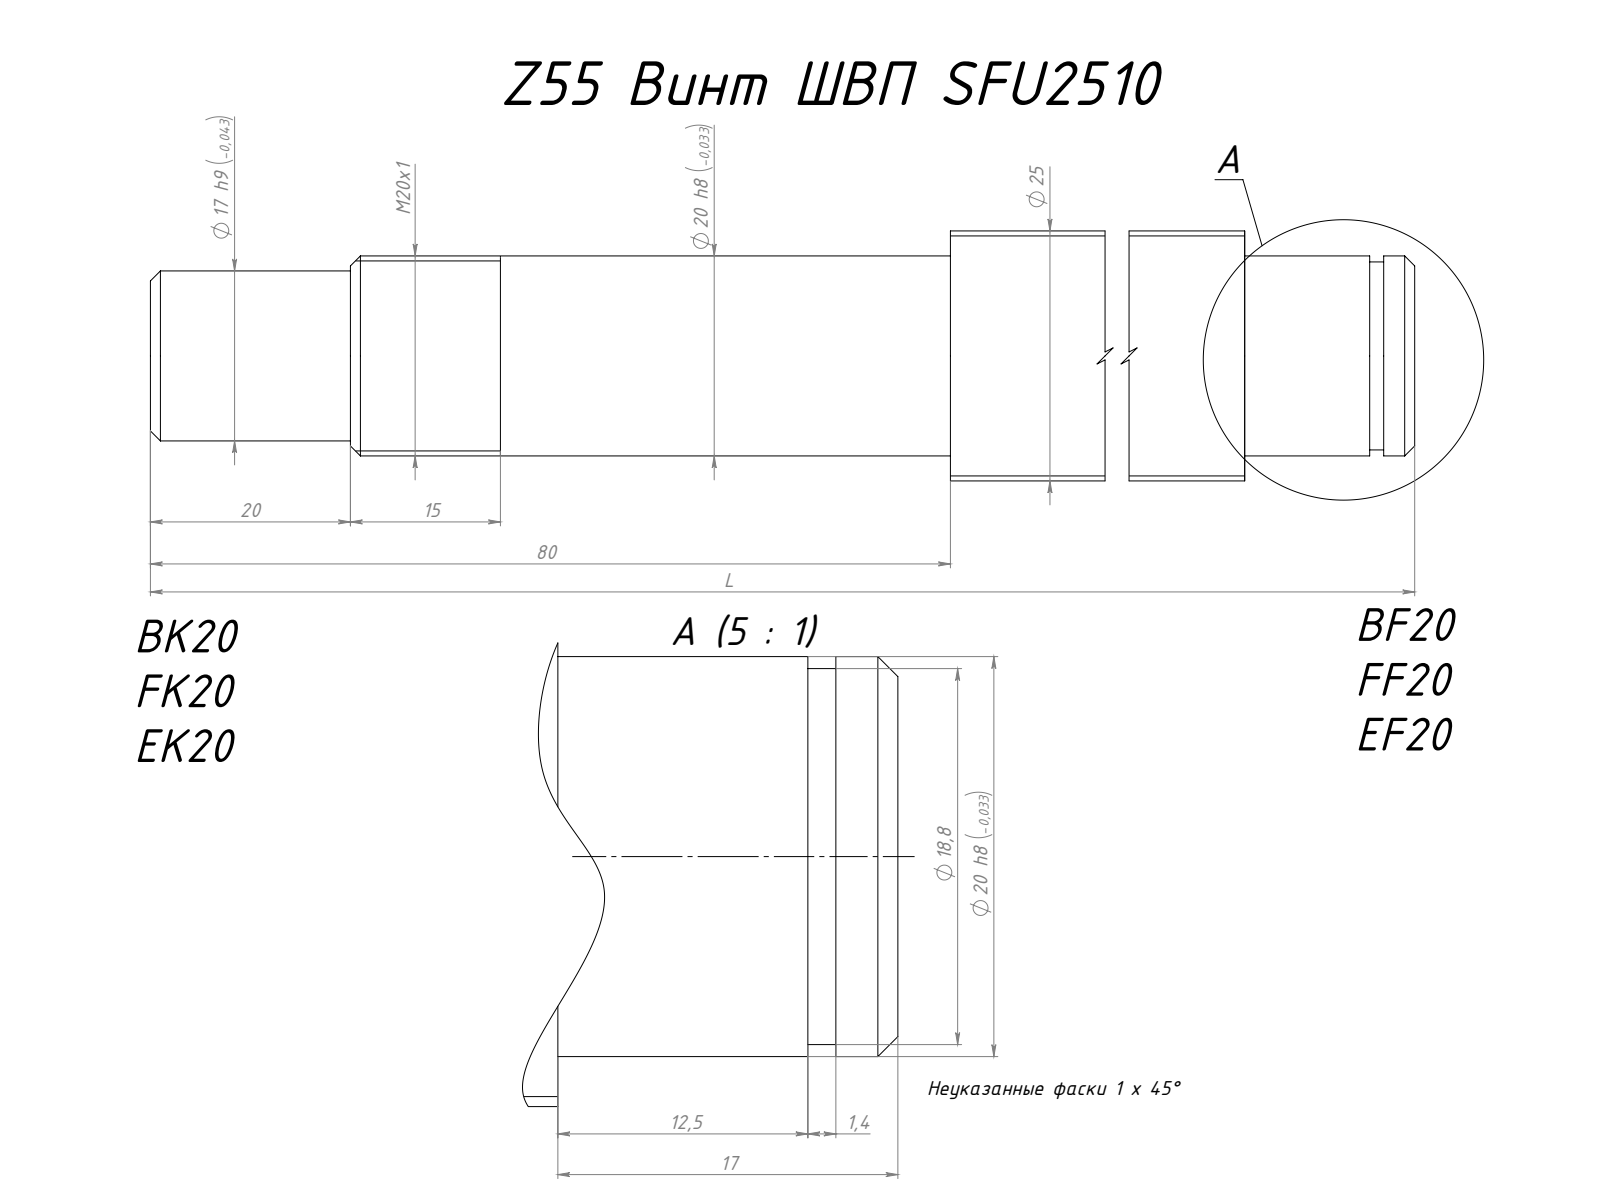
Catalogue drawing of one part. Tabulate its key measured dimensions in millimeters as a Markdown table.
| quantity | value |
| --- | --- |
| part name | Z55 Винт ШВП SFU2510 - токарная обработка BK, BF, FK, FF, EK, EF-20 |
| STEP written by | SolidWorks 2026 (AUTOMOTIVE_DESIGN) |
| units | millimeters |
| bodies | 1 solid, 25 faces (7 planar, 12 cylindrical, 6 other) |
| overall size | 3000 × 25 × 25 |
| volume | 1 454 000 mm³ |
| surface area | 234 848 mm² |
| round bosses / shafts (diameter × count) | 25 × 1, 20 × 1, 18.8 × 1, 17 × 1 |
| main face-to-face distances | 17, 2983, 3000, 80, 2903, 2920, 2995.5, 2915.5, 12.5, 4.5 |
